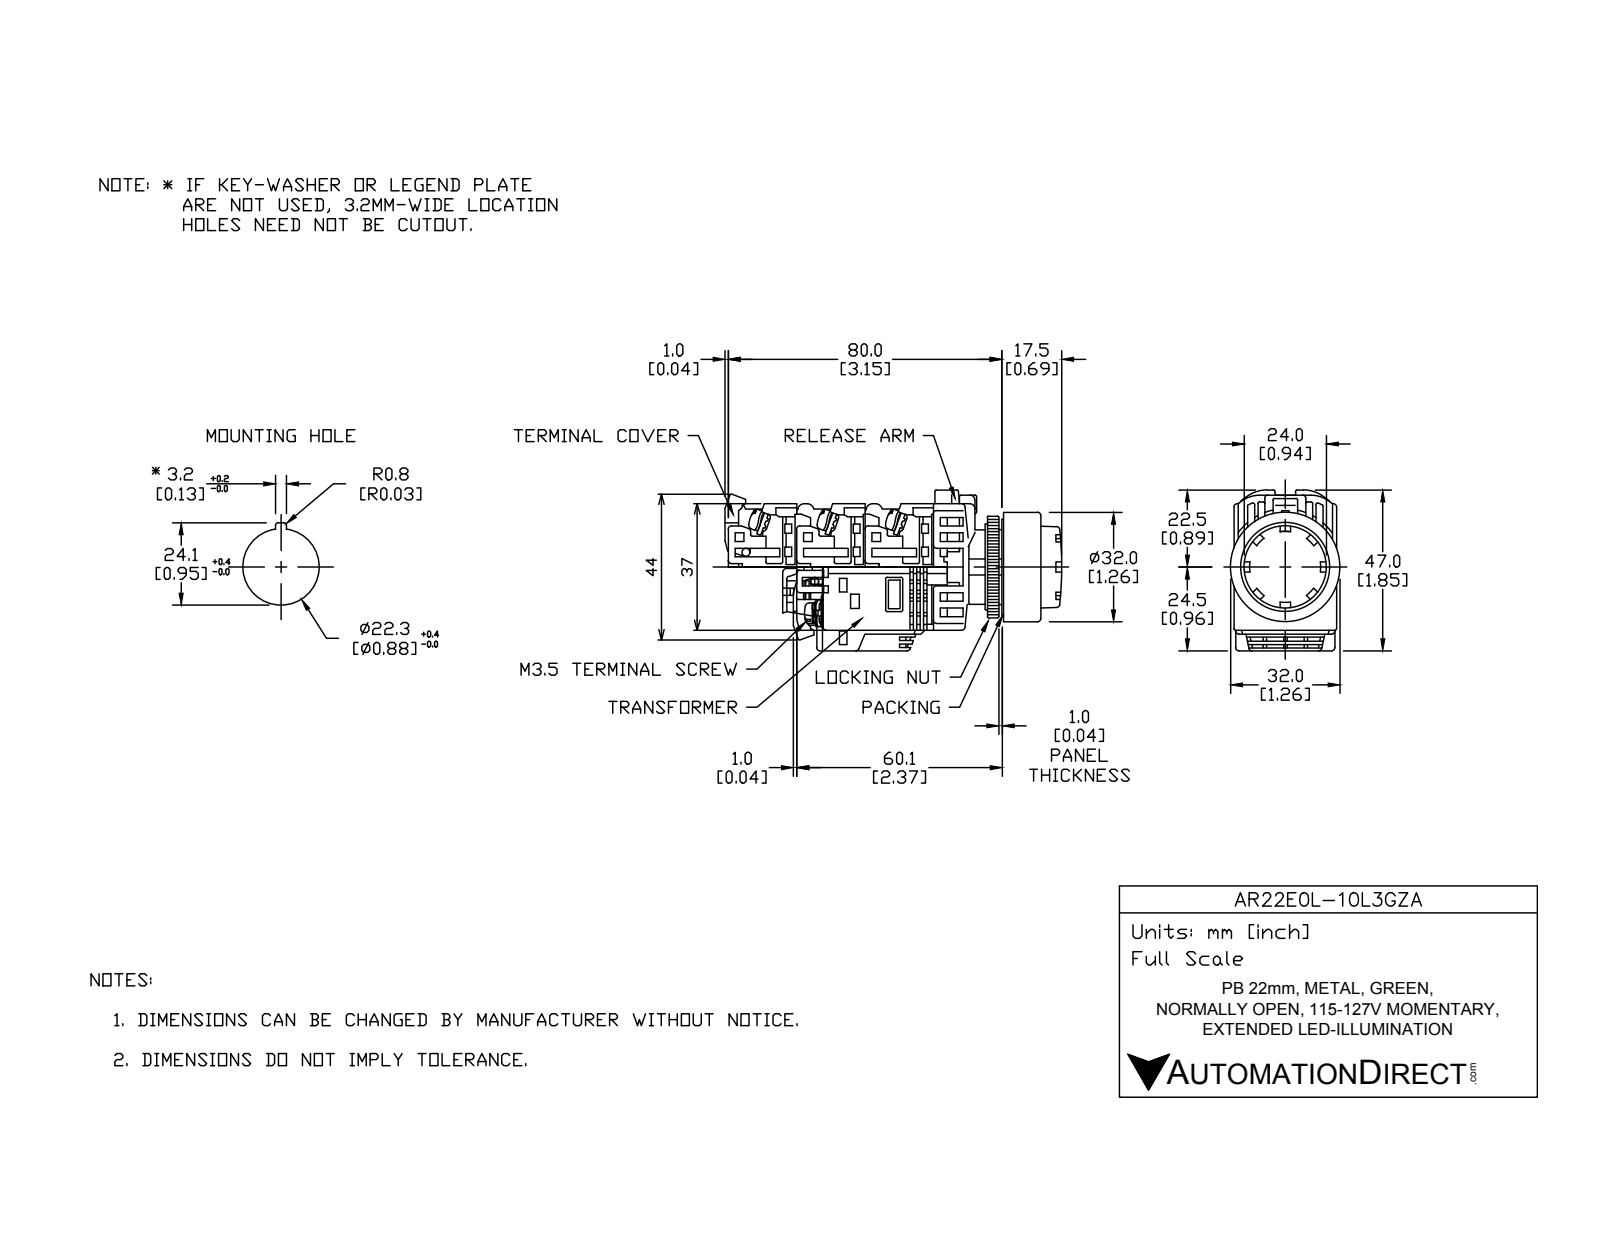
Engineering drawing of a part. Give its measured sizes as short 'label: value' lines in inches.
name: AR22E0L-10L3GZA
written by: SolidWorks 2017 (AUTOMOTIVE_DESIGN)
unit: in
bodies: 18 solids, 475 faces (329 planar, 111 cylindrical, 35 other)
size: 2.333 × 1.725 × 1.26
volume: 2.396 in³; area: 38.05 in²
holes: 1× ⌀0.858, 1× ⌀0.866, 1× ⌀0.984, 1× ⌀1.22
bosses: 4× ⌀0.197, 1× ⌀1.26, 1× ⌀1.201, 1× ⌀1.173, 1× ⌀0.945, 1× ⌀0.937, 1× ⌀0.856, 1× ⌀0.669
rounds: 39× R0.02, 8× R0.069, 4× R0.197, 2× R0.157, 1× R0.653, 1× R0.693
face distances: 0.039, 0.709, 1.122, 1.909, 0.787, 1.142, 0.118, 0.079, 0.827, 0.02
